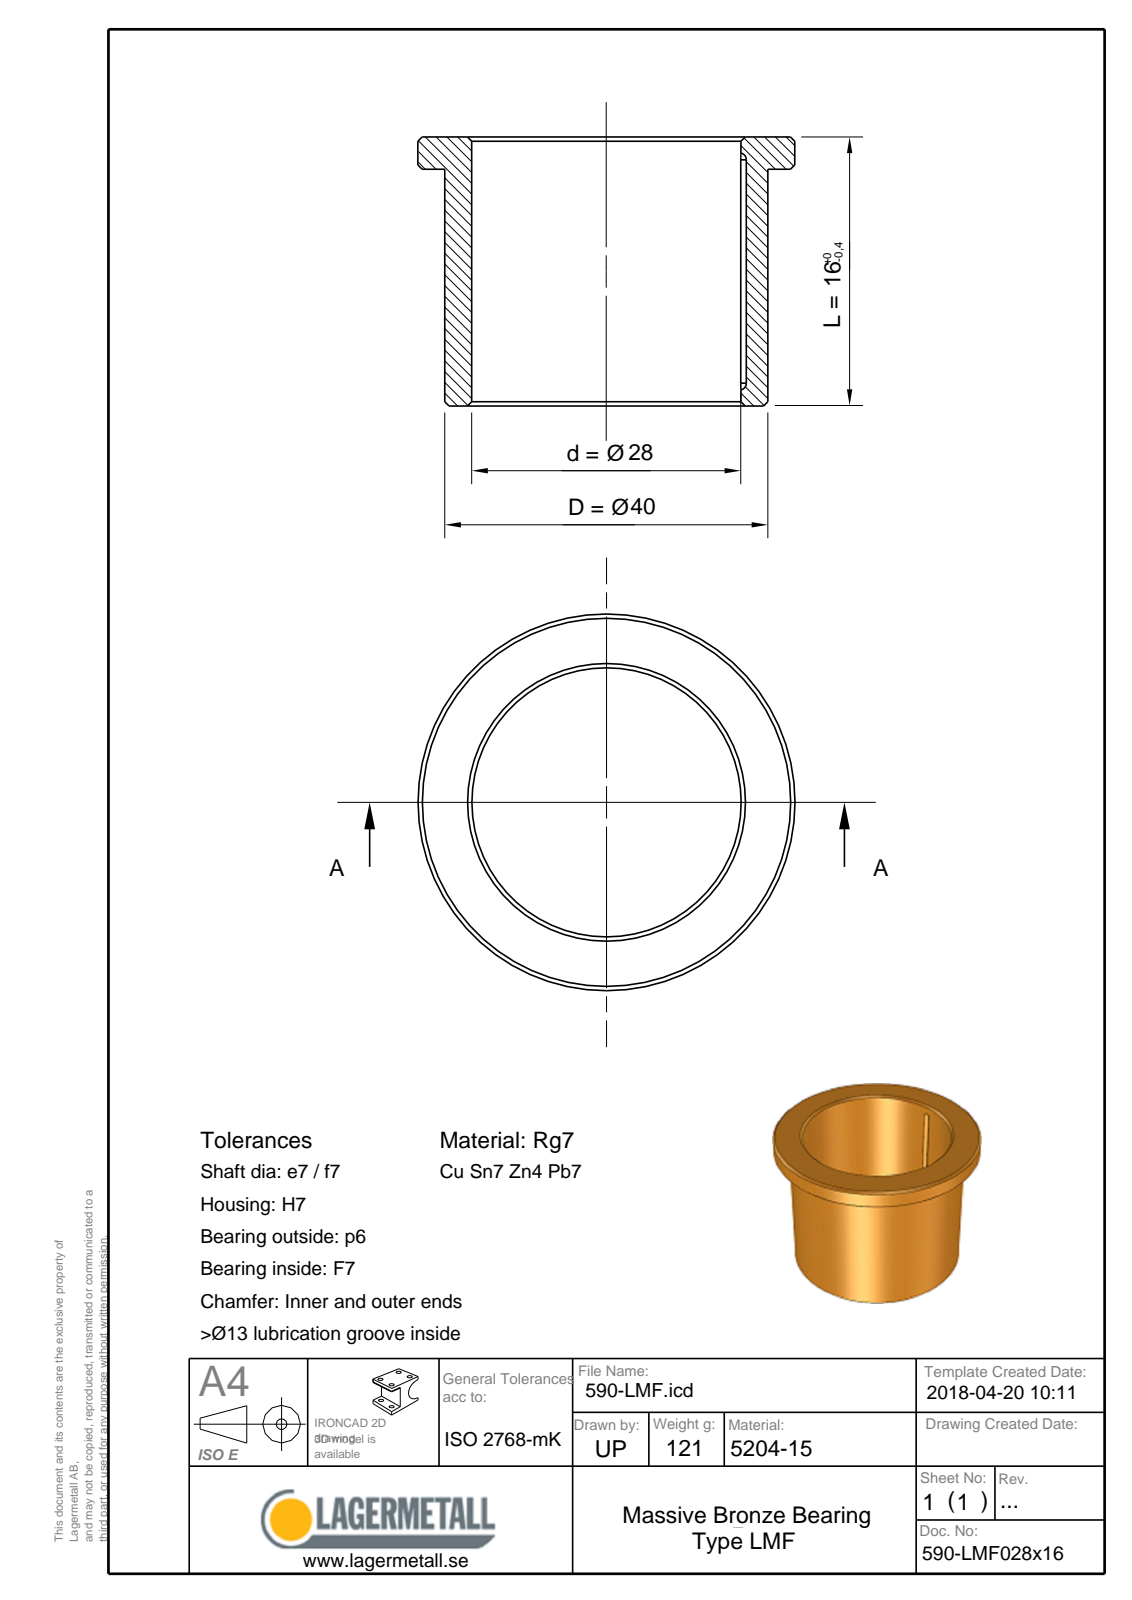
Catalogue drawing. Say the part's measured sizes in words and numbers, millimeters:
The part is named "590-LMF028x16". Its 3-D file was written by "Spatial InterOp 3D (CONFIG_CONTROL_DESIGN)". It is 1 solid with 16 faces: 4 planar, 5 cylindrical and 7 other. Overall it measures 50 by 50 by 16 millimeters. Its volume is 13 693 cubic millimeters and its surface area 6 102 square millimeters. Round holes: 1 of diameter 28. Round bosses or shafts: 1 of diameter 50, 1 of diameter 40. Partial cylindrical surfaces (rounded edges, fillets, slot ends): 2 of radius 1.25. The main face-to-face distances are 5, 11, 16.
